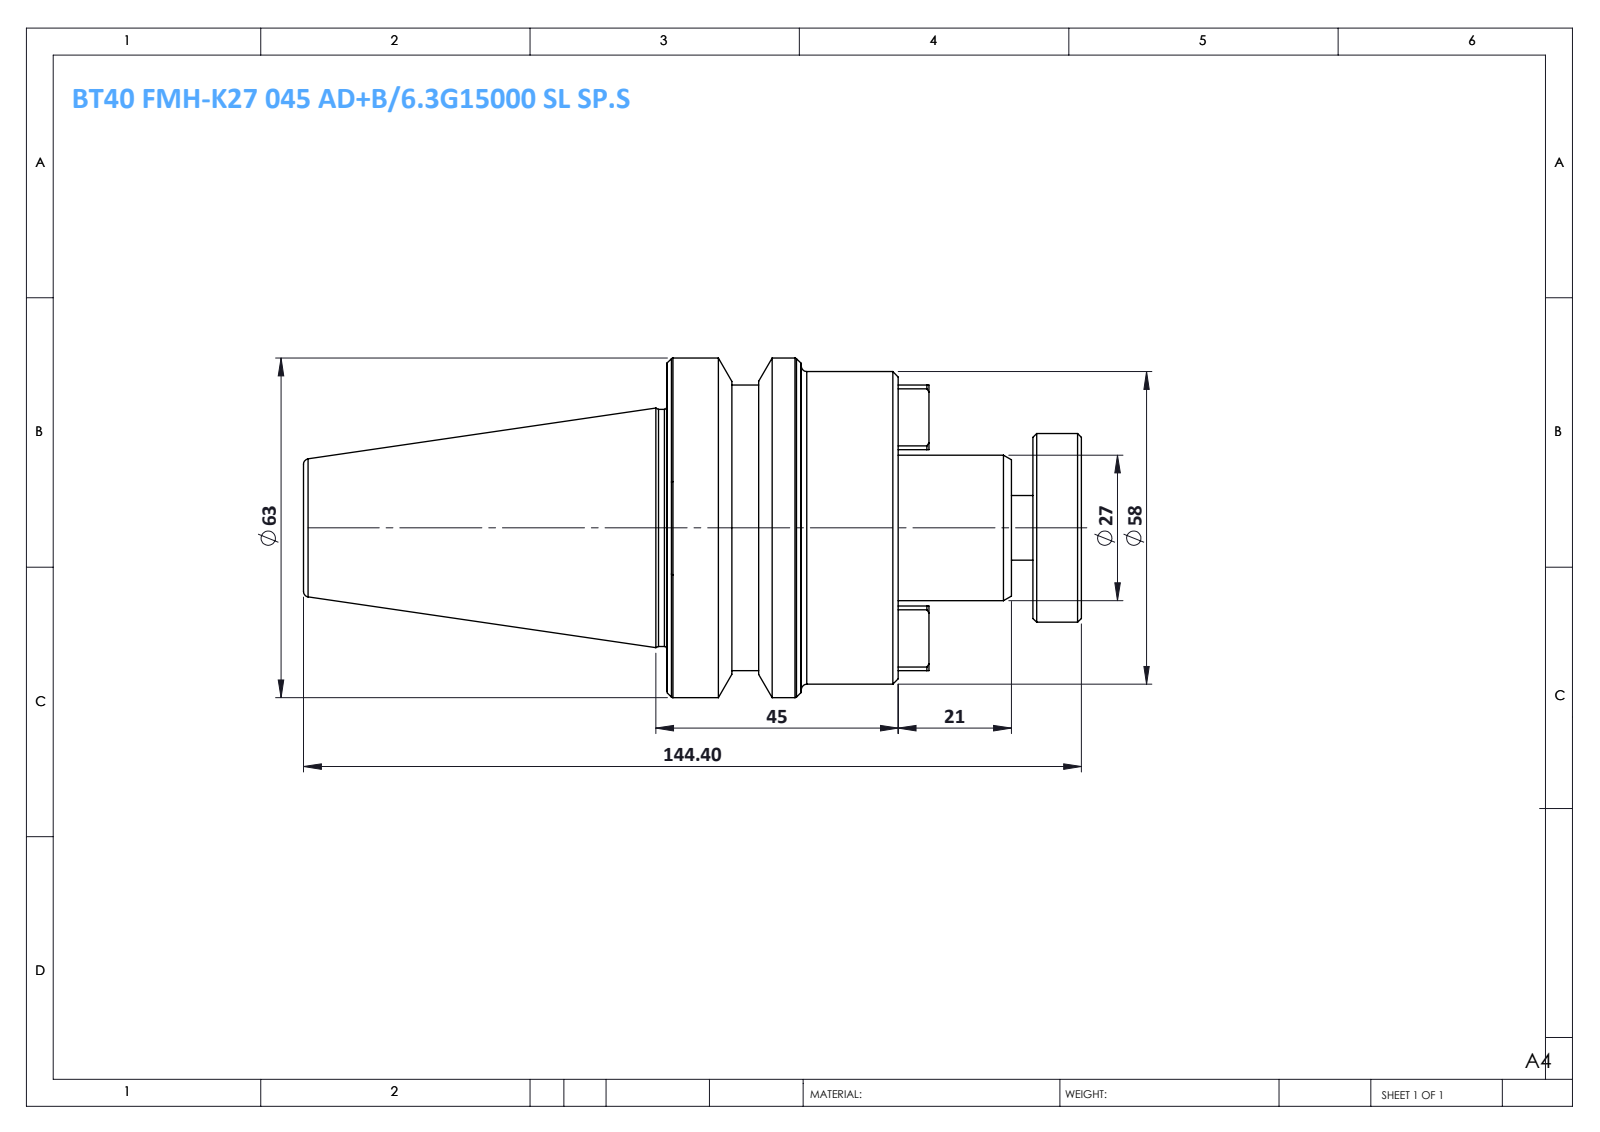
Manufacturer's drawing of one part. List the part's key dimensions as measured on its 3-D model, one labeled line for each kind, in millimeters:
Part name (STEP PRODUCT): BT40 FMH27 045 AD-6.3G15000 SL SP
STEP written by: SolidWorks 2014 (CONFIG_CONTROL_DESIGN)
Units: millimetres
Bodies: 1 solid, 91 faces (35 planar, 16 cylindrical, 40 other)
Overall size (bounding box): 144.4 × 63 × 63
Volume: 208 518 mm³ · Surface area: 26 421 mm²
Round bosses / shafts (diameter × count): ⌀63 ×1, ⌀58 ×1, ⌀53 ×1, ⌀44 ×1, ⌀35 ×1, ⌀27 ×1, ⌀12 ×1
Main face-to-face distances: 43, 34, 77, 25, 9, 68, 144.4, 135.4, 110.4, 67.4
